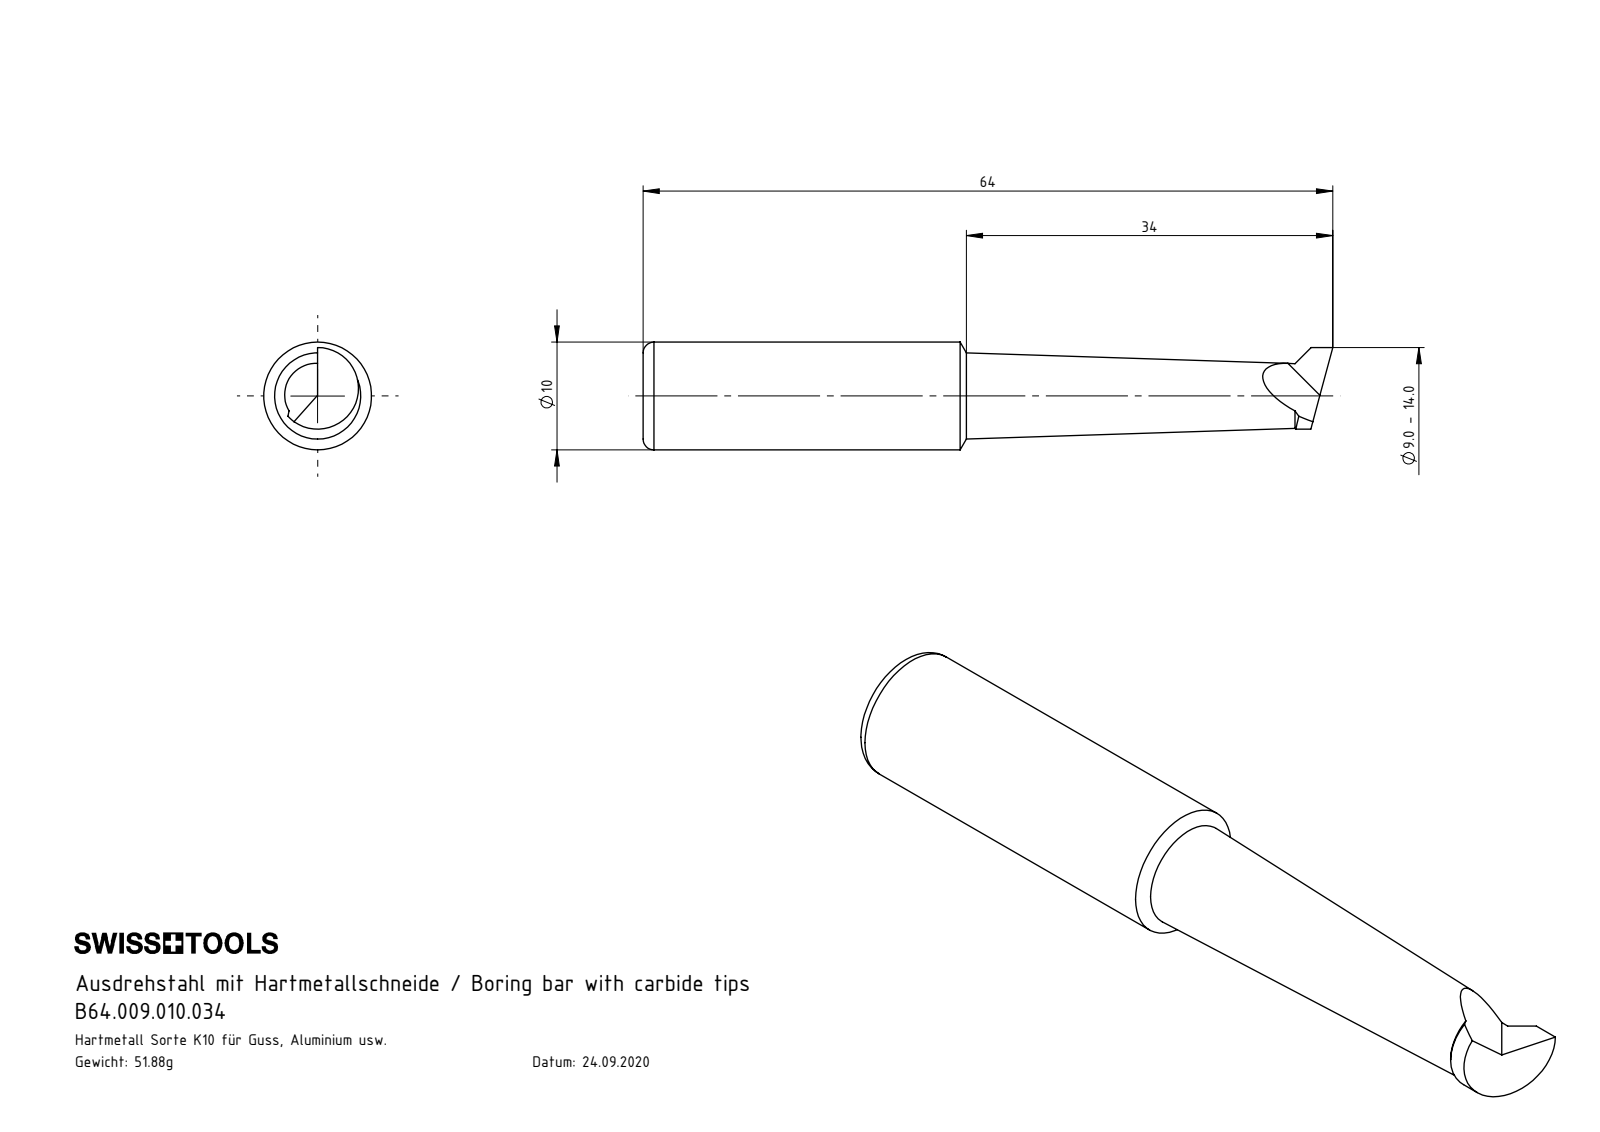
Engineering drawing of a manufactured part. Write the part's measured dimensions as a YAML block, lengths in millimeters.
part_name: "B64.009.010.034"
step_written_by: "SolidWorks 2022 (CONFIG_CONTROL_DESIGN)"
units: millimeters
bodies: {solids: 1, faces: 14, planar: 4, cylindrical: 3, other: 7}
overall_size: [64, 10, 10]
volume: 3578
surface_area: 1776
round_bosses_or_shafts:
  - {diameter: 10, count: 1}
partial_cylinders:
  - {radius: 3.79, count: 1}
